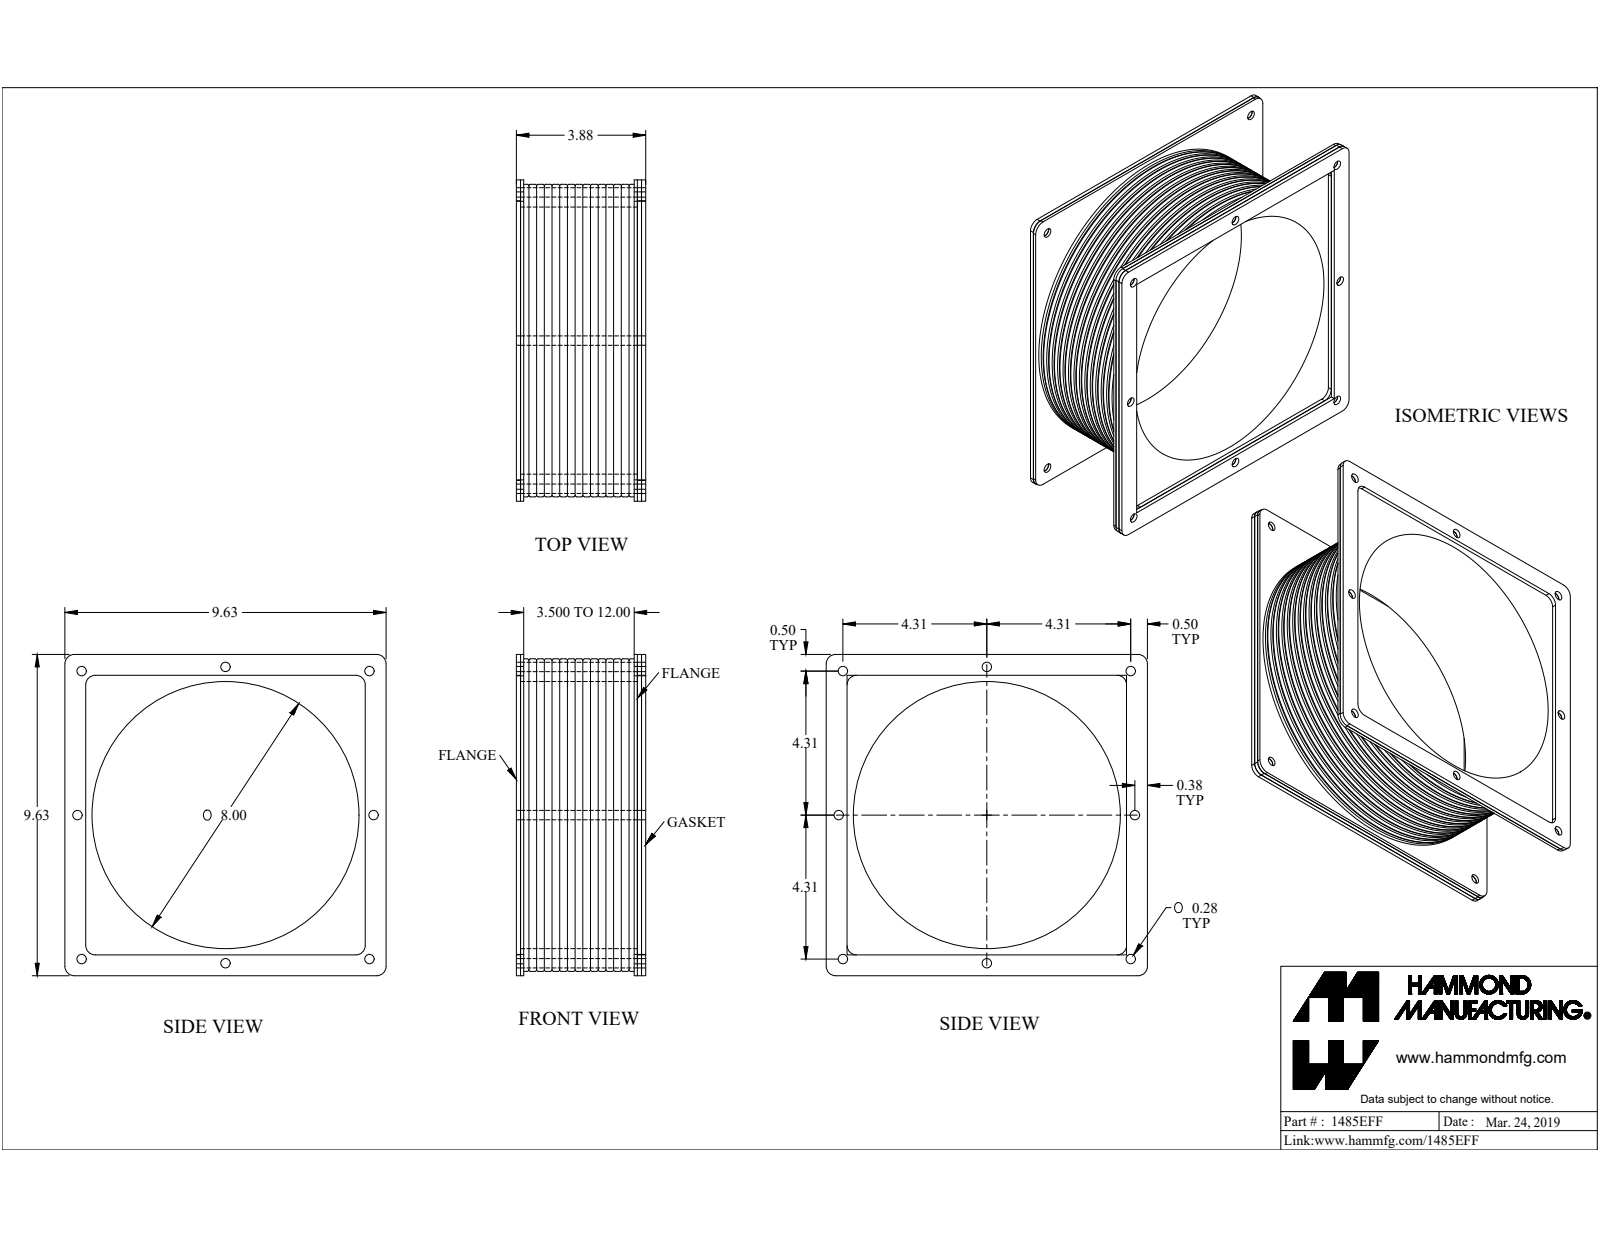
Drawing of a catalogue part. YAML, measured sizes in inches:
part_name: "1485EFF"
step_written_by: "SolidWorks 2019 (CONFIG_CONTROL_DESIGN)"
units: inches
bodies: {solids: 4, faces: 150, planar: 42, cylindrical: 80, other: 28}
overall_size: [9.625, 9.625, 3.875]
volume: 76.33
surface_area: 520.5
round_holes:
  - {diameter: 0.281, count: 8}
  - {diameter: 0.281, count: 8}
  - {diameter: 8, count: 1}
round_bosses_or_shafts:
  - {diameter: 9.362, count: 1}
partial_cylinders:
  - {radius: 0.281, count: 8}
  - {radius: 0.313, count: 4}
face_to_face_distances: [0.125, 3.625, 3.5, 0.095, 3.405, 0.22, 3.53, 3.31, 3.75, 3.875]
hole_center_spacings: [4.315, 9.755, 4.437, 6.099, 6.276, 8.625, 8.875, 12.198]
